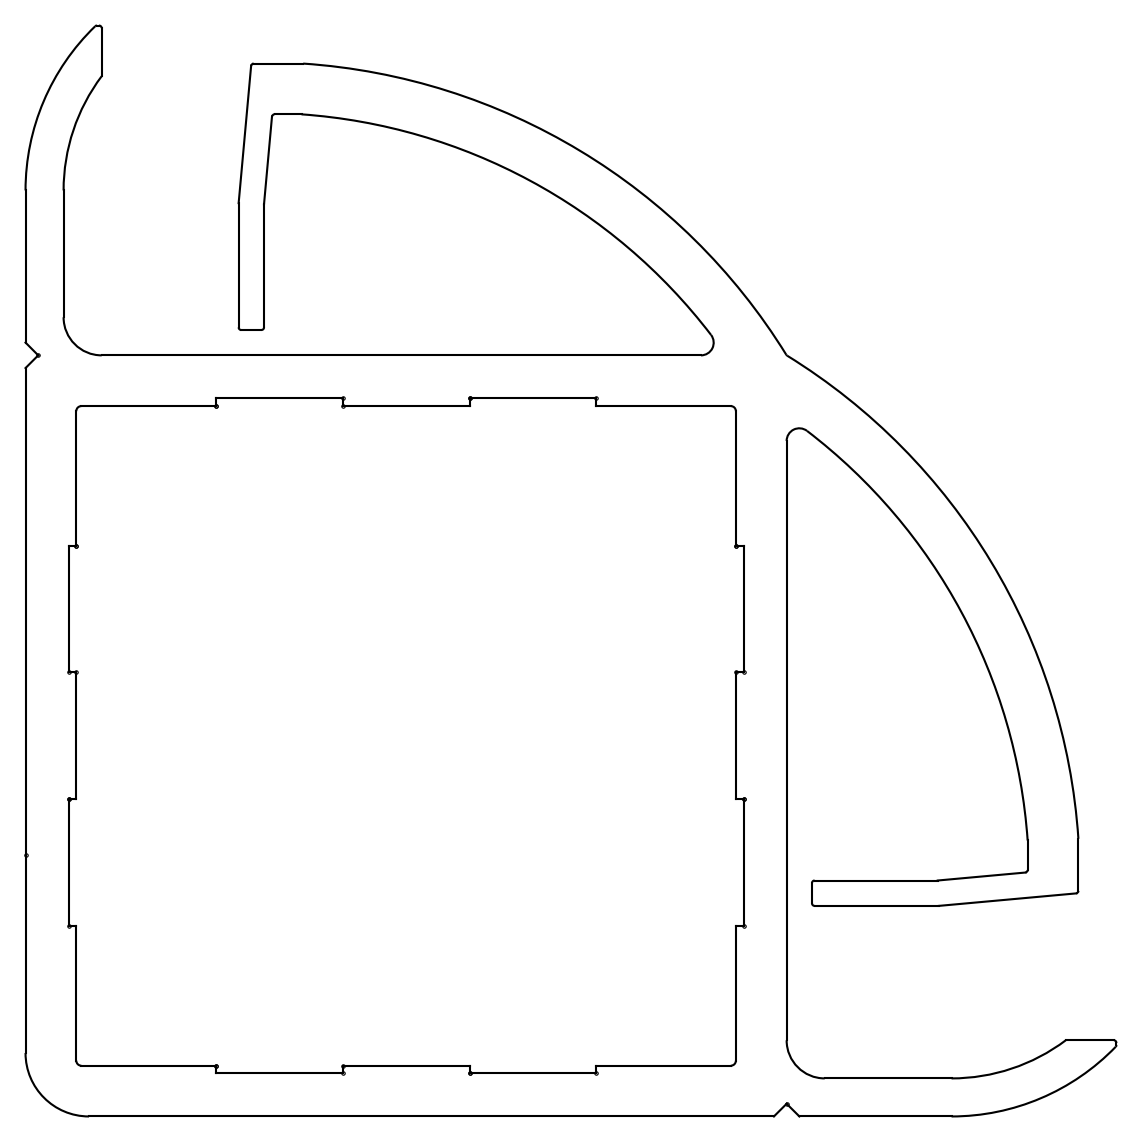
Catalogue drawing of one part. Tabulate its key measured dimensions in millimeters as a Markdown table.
| quantity | value |
| --- | --- |
| STEP written by | THINKDESIGN (CONFIG_CONTROL_DESIGN) |
| units | millimeters |
| bodies | 1 solid, 98 faces (68 planar, 30 cylindrical, 0 other) |
| overall size | 100 × 43 × 43 |
| volume | 36 139 mm³ |
| surface area | 41 155 mm² |
| partial cylindrical surfaces (radius × count) | 0.1 × 13, 0.2 × 4, 0.5 × 2, 1.5 × 2, 7.5 × 2, 9 × 2, 22.31 × 2, 24.31 × 2 |
| main face-to-face distances | 2, 28, 30, 1.7, 28.3, 26.3, 26, 1, 26.6, 1.5 |
